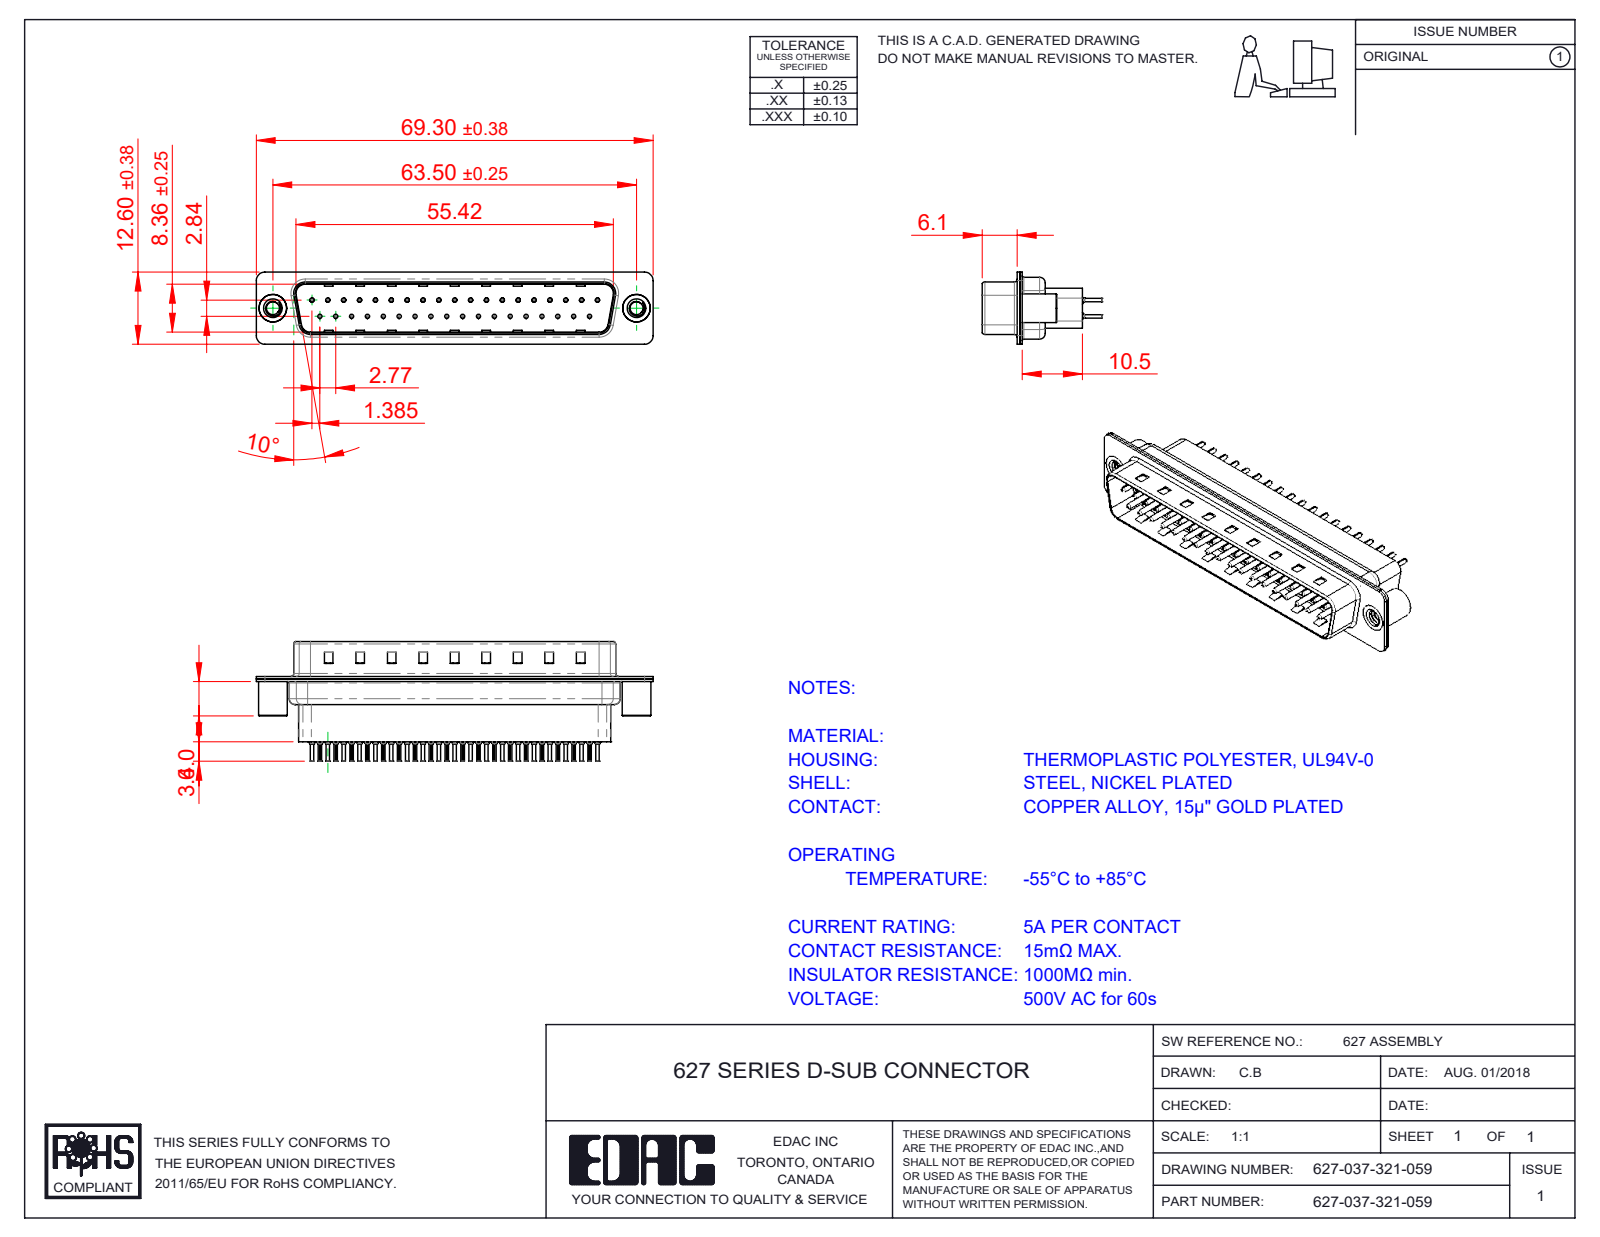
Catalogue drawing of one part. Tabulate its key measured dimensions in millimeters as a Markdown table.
| quantity | value |
| --- | --- |
| part name | 627-037-321-059; 627 Shell Rear_37 Contacts; 627 Shell Front_37 Contacts; 627 Contact Row 1_21H (+3 more) |
| STEP written by | SolidWorks 2020 (CONFIG_CONTROL_DESIGN) |
| units | millimeters |
| bodies | 42 solids, 4060 faces (1091 planar, 1530 cylindrical, 1439 other) |
| overall size | 69.3 × 20.8 × 12.6 |
| volume | 5 403 mm³ |
| surface area | 13 750 mm² |
| round holes (diameter × count) | 0.2 × 37, 0.35 × 37, 1.1 × 37, 1.6 × 37, 2.26 × 2, 4 × 2, 4.8 × 2 |
| round bosses / shafts (diameter × count) | 2 × 37, 1.5 × 37, 0.75 × 37, 0.6 × 37, 5 × 2, 4.9 × 2 |
| partial cylindrical surfaces (radius × count) | 0.1 × 74, 1.5 × 16, 2 × 12, 0.5 × 8, 1.6 × 8, 0.25 × 4, 0.6 × 4, 0.65 × 4 |
| main face-to-face distances | 0.4, 0.82, 9.58, 0.68, 7.68, 0.45, 1.5, 1.08, 8.08, 8.76 |
| hole center spacings | 3.16, 2.77, 5.54, 8.31, 5.04, 10.1, 11.08, 12.78 |
